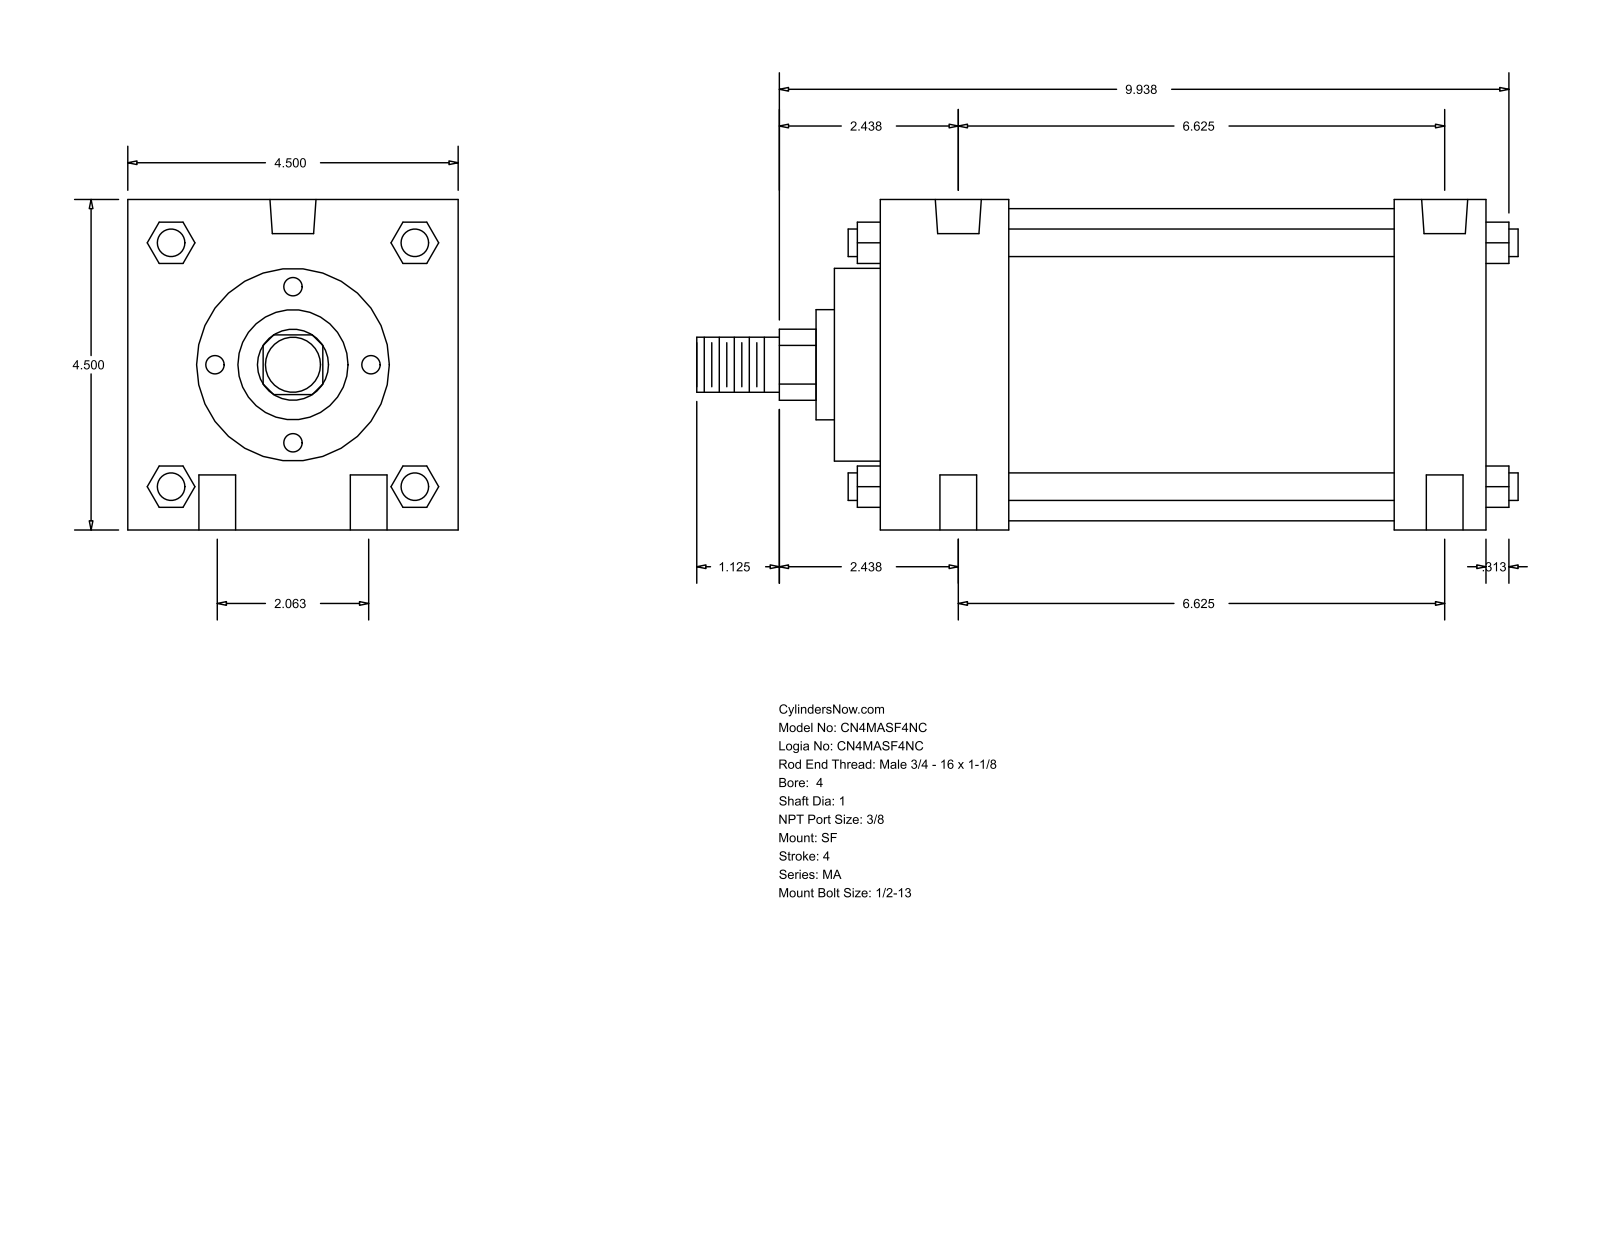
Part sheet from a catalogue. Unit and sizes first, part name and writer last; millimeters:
Units: millimetres
Overall size (bounding box): 284.16 × 114.3 × 114.3
Round holes (diameter × count): ⌀12.7 ×4, ⌀11.11 ×2, ⌀15.93 ×2
Round bosses / shafts (diameter × count): ⌀9.53 ×4, ⌀107.95 ×1, ⌀66.67 ×1, ⌀38.1 ×1, ⌀25.4 ×1, ⌀19.05 ×1
Partial cylindrical surfaces — rounded edges, fillets, slot ends (radius × count): R12.29 ×1
Main face-to-face distances: 114.3, 209.55, 177.8, 31.75, 44.46, 133.34, 165.09, 225.42, 15.87, 60.33
Hole centre spacings: 26.19, 170.31, 168.28, 52.38, 176.24, 158.76
Bodies: 0 solids, 126 faces (95 planar, 31 cylindrical, 0 other)
Part name (STEP PRODUCT): MA_SF__0400_1
STEP written by: GSSL Pune (CONFIG_CONTROL_DESIGN)
